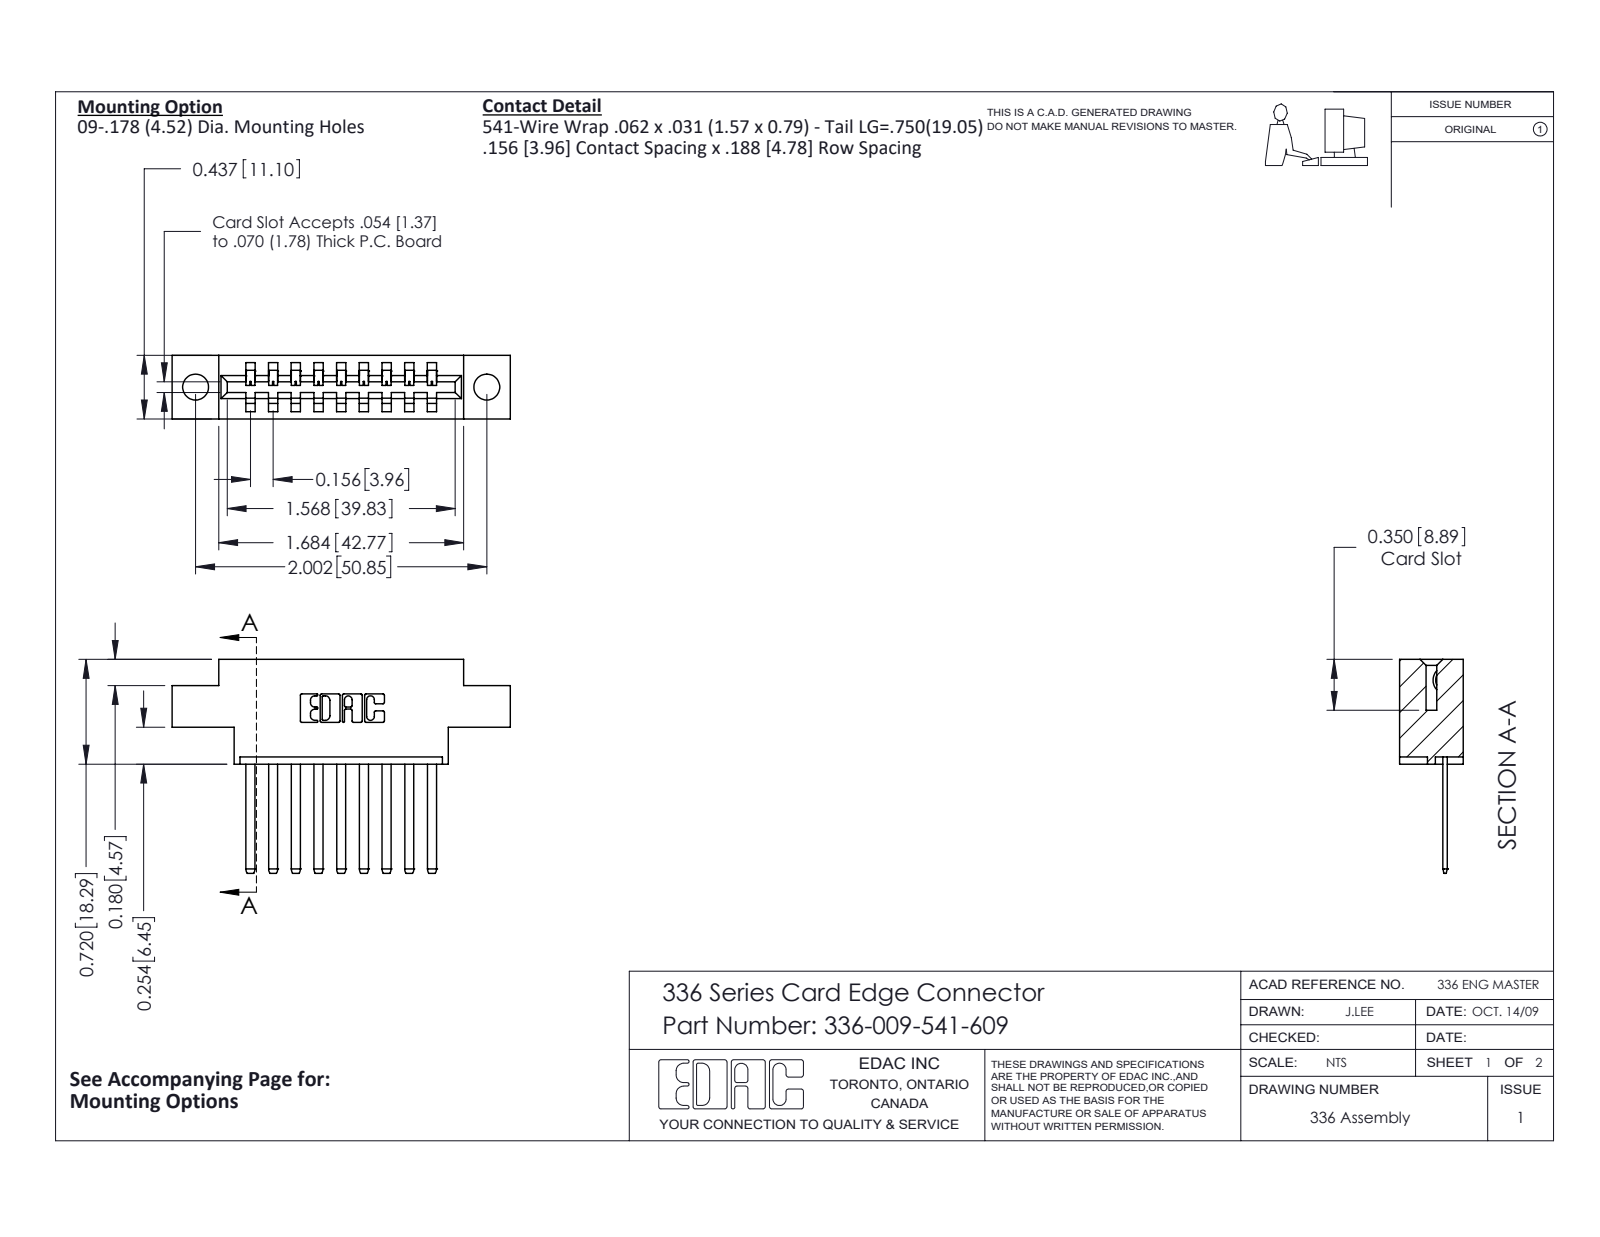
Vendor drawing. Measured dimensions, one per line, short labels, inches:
name: 336 Part_Offset - .178 Dia - TH; 336-290-001_336-290-541; 336-009-541-609
written by: SolidWorks 2020 (CONFIG_CONTROL_DESIGN)
unit: in
bodies: 10 solids, 568 faces (380 planar, 188 cylindrical, 0 other)
size: 2.325 × 1.47 × 0.437
volume: 0.458 in³; area: 11.94 in²
holes: 2× ⌀0.178
rounds: 22× R0.01, 18× R0.004, 18× R0.056, 6× R0.007, 6× R0.031, 3× R0.026, 2× R0.022, 2× R0.04
face distances: 0.156, 0.437, 0.624, 0.312, 0.468, 0.78, 0.22, 0.376, 0.312, 0.404
hole spacings: 2.002
